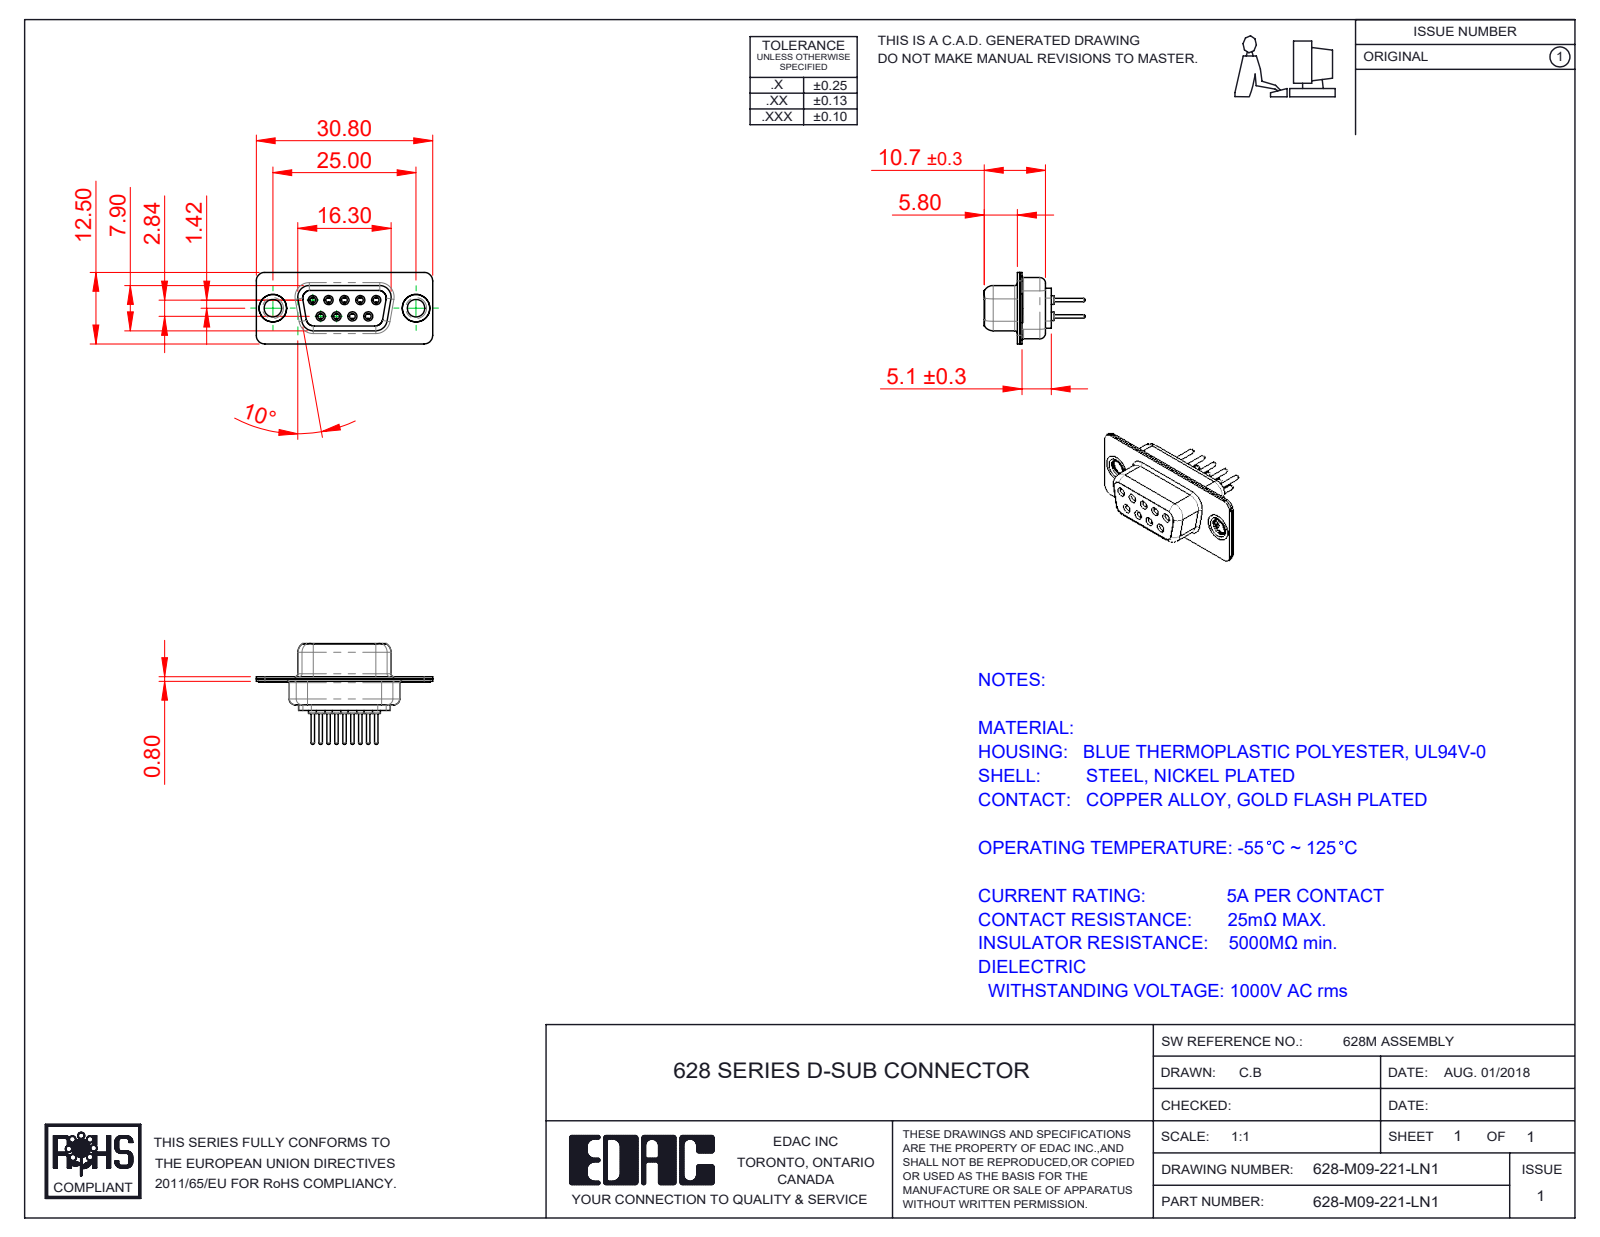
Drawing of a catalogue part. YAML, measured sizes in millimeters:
part_name: "628M Housing_09 Contacts; 628-M09-221-LN1; 628M Contact Row 2_21; 628M Thru Hole Rivet (+3 more)"
step_written_by: "SolidWorks 2020 (CONFIG_CONTROL_DESIGN)"
units: millimeters
bodies: {solids: 14, faces: 748, planar: 202, cylindrical: 292, other: 254}
overall_size: [30.8, 17.6, 12.5]
volume: 1624
surface_area: 4277
round_holes:
  - {diameter: 1, count: 9}
  - {diameter: 1.1, count: 9}
  - {diameter: 1.7, count: 9}
  - {diameter: 1.8, count: 9}
  - {diameter: 2, count: 9}
  - {diameter: 3.05, count: 2}
  - {diameter: 4, count: 2}
  - {diameter: 4.8, count: 2}
round_bosses_or_shafts:
  - {diameter: 2.2, count: 9}
  - {diameter: 1.6, count: 9}
  - {diameter: 1.5, count: 9}
  - {diameter: 0.6, count: 9}
  - {diameter: 5, count: 2}
  - {diameter: 4.9, count: 2}
  - {diameter: 3.55, count: 2}
partial_cylinders:
  - {radius: 1.5, count: 16}
  - {radius: 2, count: 12}
  - {radius: 1.35, count: 8}
  - {radius: 1.6, count: 8}
  - {radius: 0.25, count: 4}
  - {radius: 0.5, count: 4}
  - {radius: 0.6, count: 4}
  - {radius: 0.65, count: 4}
face_to_face_distances: [0.4, 1.4, 0.45, 8.45, 0.8, 8.9, 1.8, 1, 6.2, 1.35]
hole_center_spacings: [3.16, 2.77, 5.54, 5.03, 5.04, 8.31, 7.1, 7.48]
